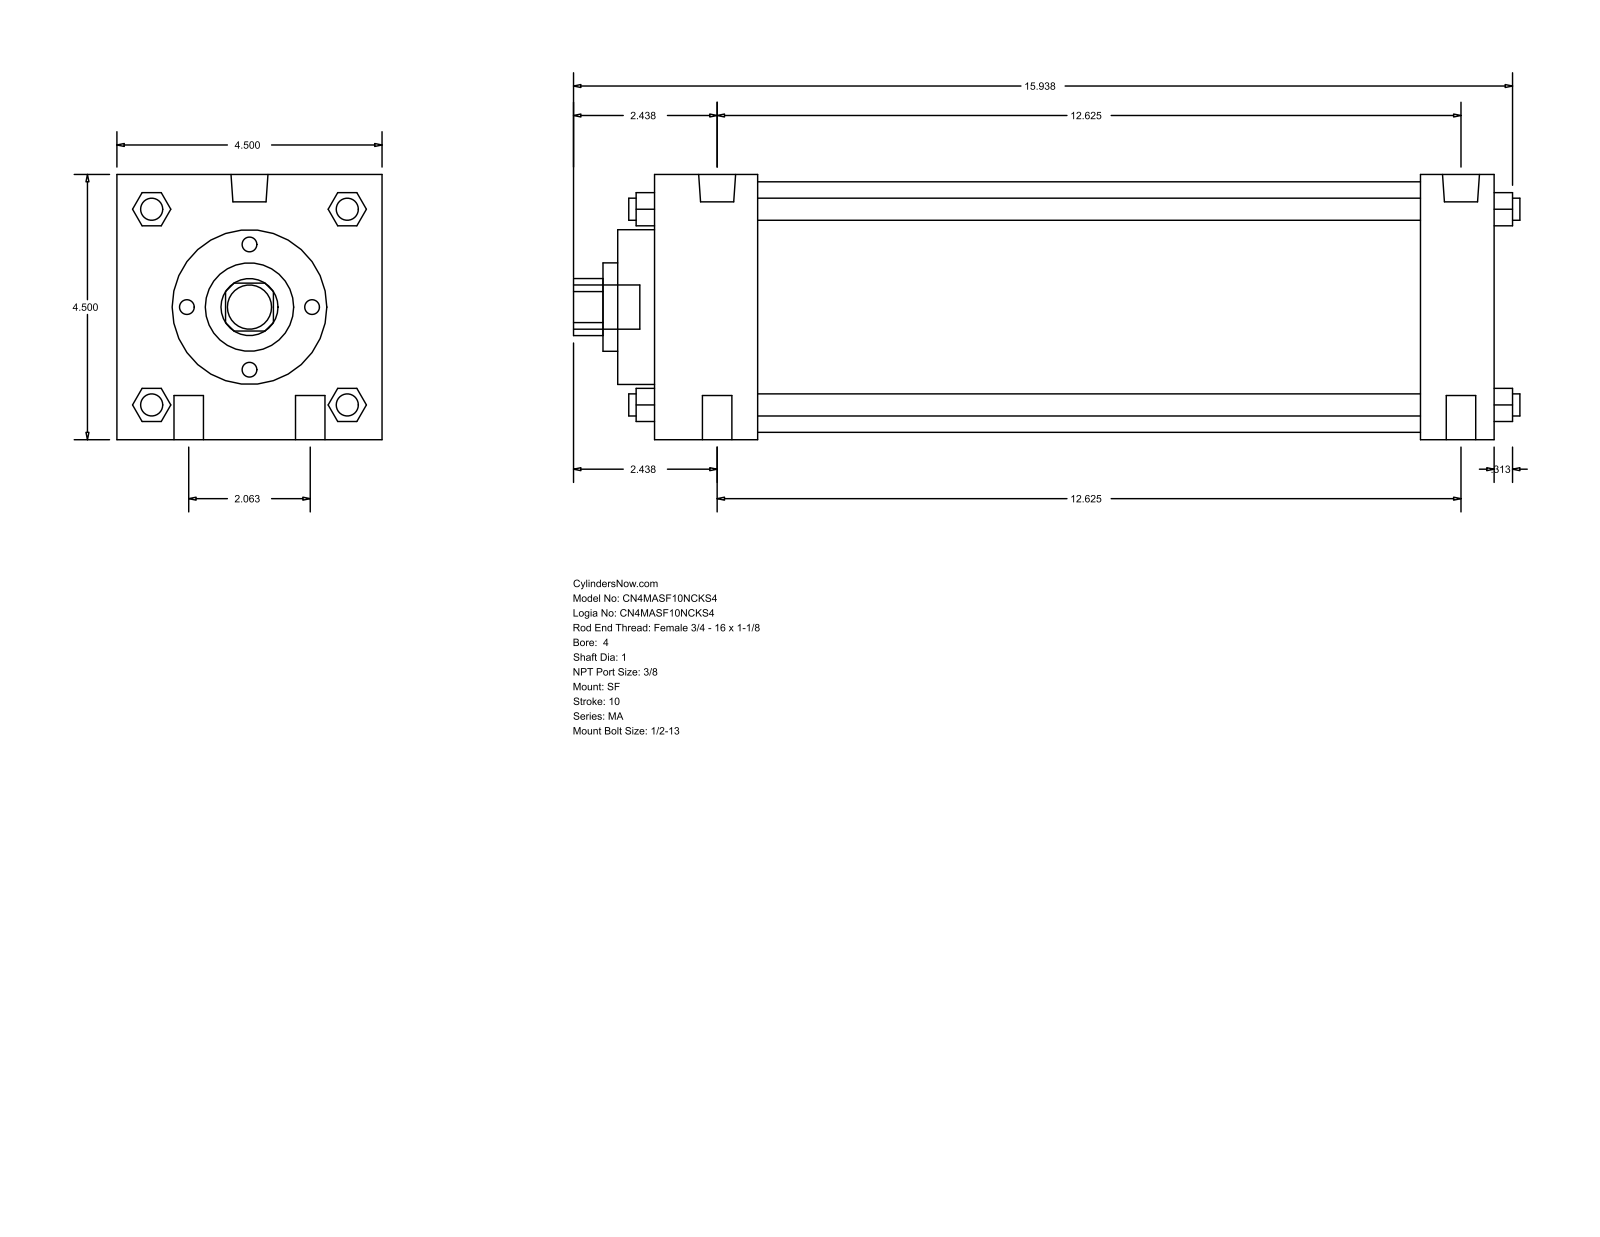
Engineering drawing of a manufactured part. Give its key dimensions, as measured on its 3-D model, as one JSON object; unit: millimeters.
{"part_name": "MA_SF__0400_1", "step_written_by": "GSSL Pune (CONFIG_CONTROL_DESIGN)", "units": "millimeters", "bodies": {"solids": 0, "faces": 126, "planar": 95, "cylindrical": 31, "other": 0}, "overall_size": [407.99, 114.3, 114.3], "round_holes": [[25.4, 1], [38.1, 1], [66.67, 1], [107.95, 1]], "round_bosses_or_shafts": [[12.7, 4], [9.53, 4], [15.93, 2], [11.11, 2], [19.05, 1]], "partial_cylinders_radius": [[12.29, 1]], "face_to_face_distances": [114.3, 361.96, 330.2, 31.76, 44.46, 285.74, 317.5, 15.87, 60.33, 346.07]}
